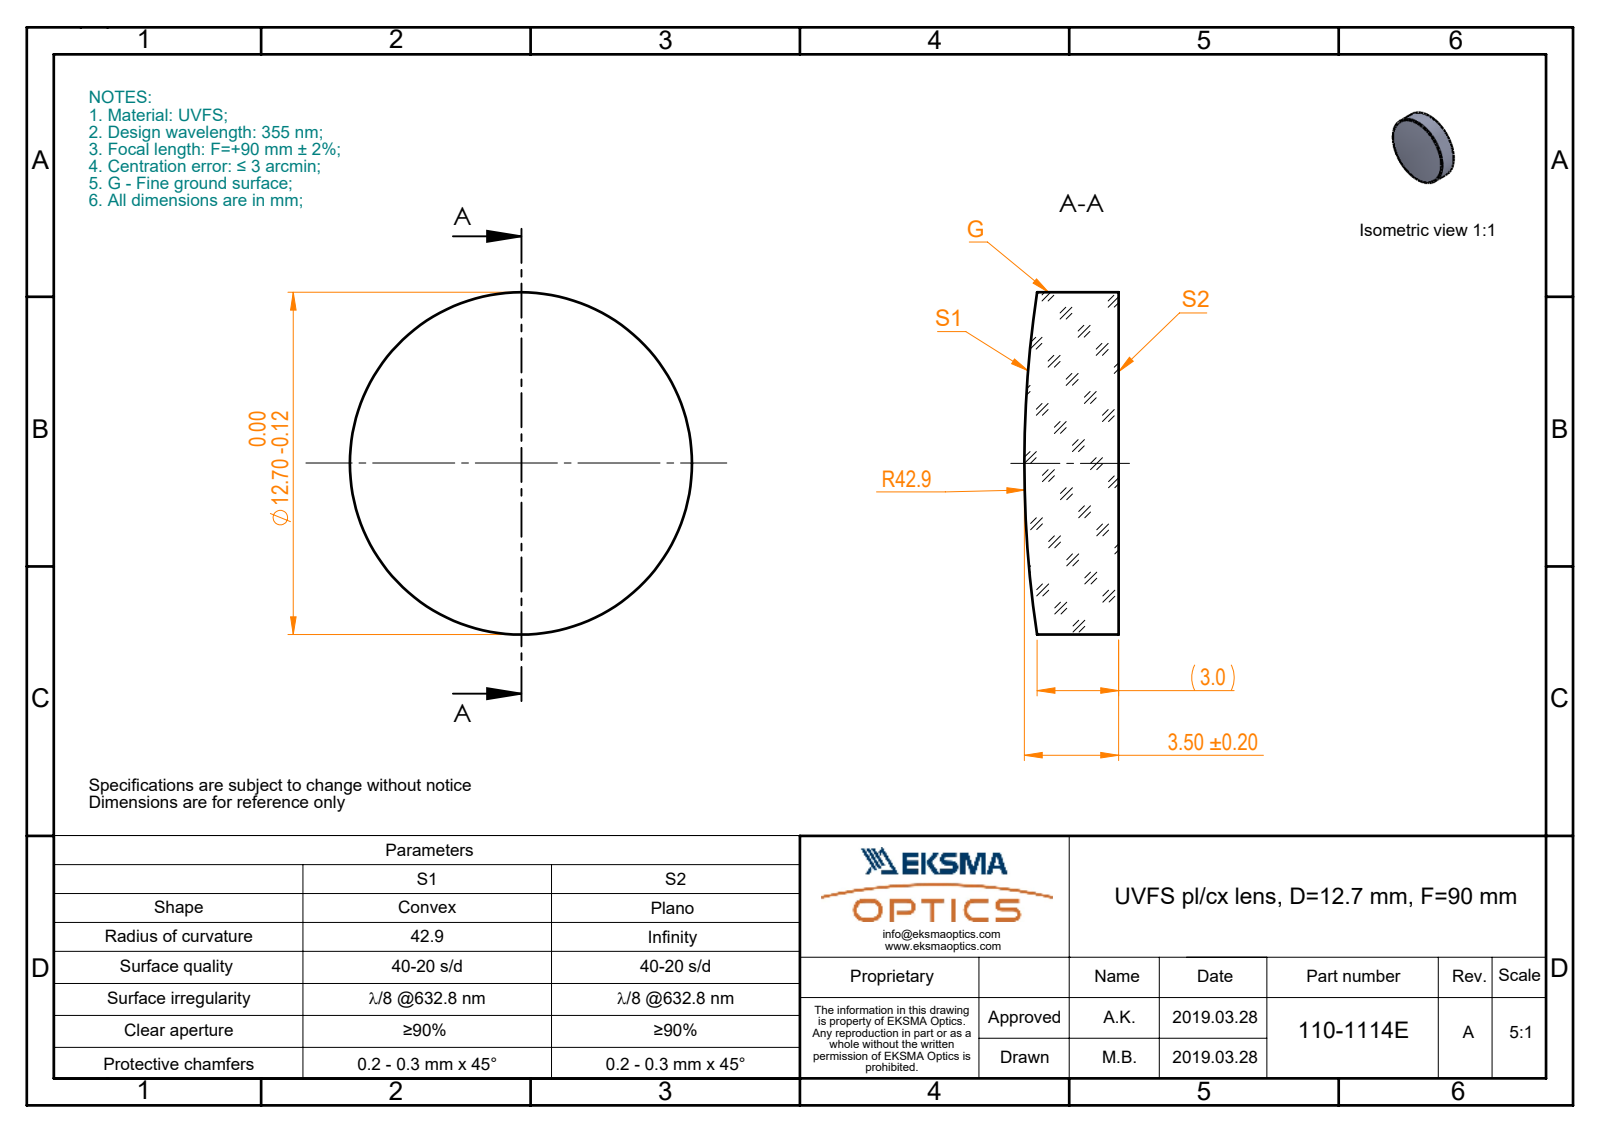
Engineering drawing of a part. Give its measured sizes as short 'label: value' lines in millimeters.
name: 110-1114E UVFS pl-cx 12.7 F90
written by: SolidWorks 2017 (CONFIG_CONTROL_DESIGN)
unit: mm
bodies: 1 solid, 5 faces (1 planar, 2 cylindrical, 2 other)
size: 12.7 × 12.7 × 3.5
volume: 413 mm³; area: 375 mm²
bosses: 1× ⌀12.7
